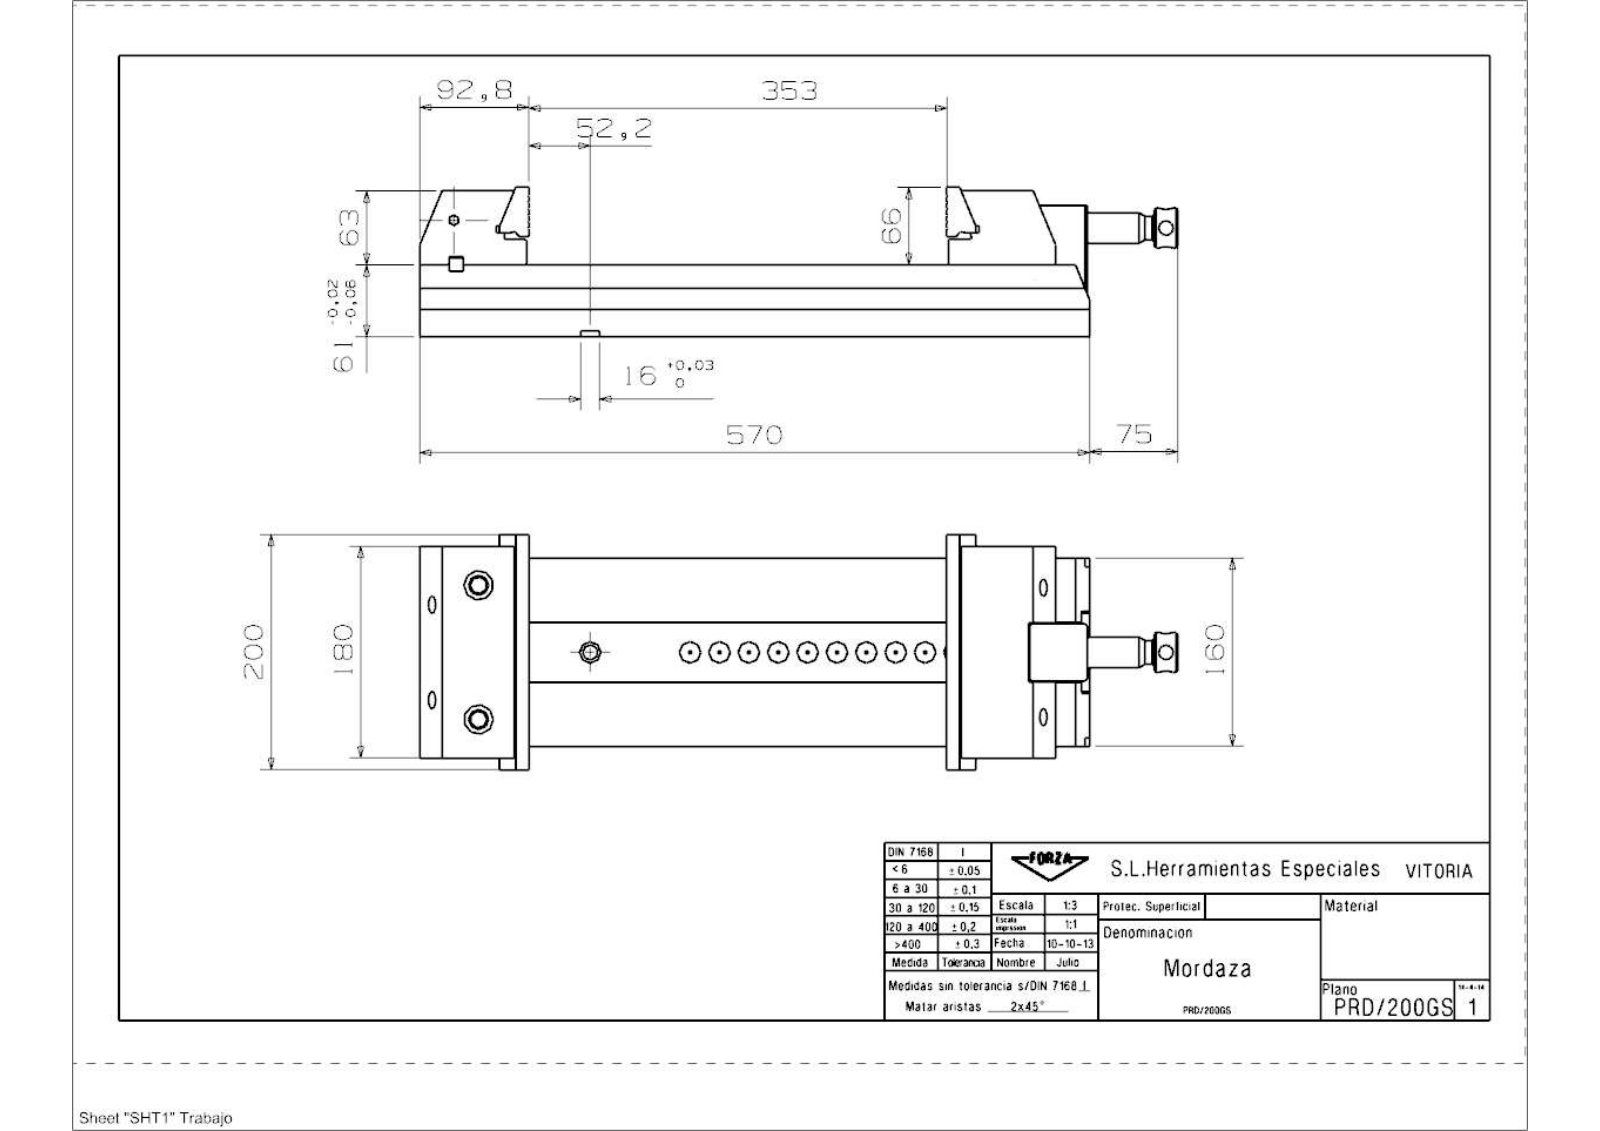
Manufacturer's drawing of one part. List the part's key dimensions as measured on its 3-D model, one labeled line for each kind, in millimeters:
Part name (STEP PRODUCT): 30150070 Montaje Taco Hus; PRD_200GS_Mordaza
STEP written by: SIEMENS PLM Software NX 9.0 (CONFIG_CONTROL_DESIGN)
Units: millimetres
Bodies: 11 solids, 478 faces (280 planar, 130 cylindrical, 68 other)
Overall size (bounding box): 645 × 200 × 126.95
Volume: 6 230 000 mm³ · Surface area: 649 701 mm²
Round holes (diameter × count): ⌀15 ×6, ⌀5.19 ×5, ⌀13 ×5, ⌀6.99 ×4, ⌀8.5 ×4, ⌀10 ×4, ⌀14.38 ×4, ⌀8.78 ×3, ⌀19 ×3, ⌀12 ×2, ⌀12.38 ×2, ⌀17 ×2
Round bosses / shafts (diameter × count): ⌀34 ×1, ⌀33.8 ×1, ⌀26 ×1, ⌀20 ×1, ⌀16.5 ×1
Partial cylindrical surfaces — rounded edges, fillets, slot ends (radius × count): R0.4 ×24, R1.5 ×4, R8 ×4, R20 ×4, R1.6 ×2, R6 ×2, R7 ×2, R4 ×1
Main face-to-face distances: 61, 29.2, 31.8, 7.5, 2, 160, 27.2, 59, 63, 124
Hole centre spacings: 14.5, 95.5, 81, 95.35, 110, 68, 16.47, 16.55
